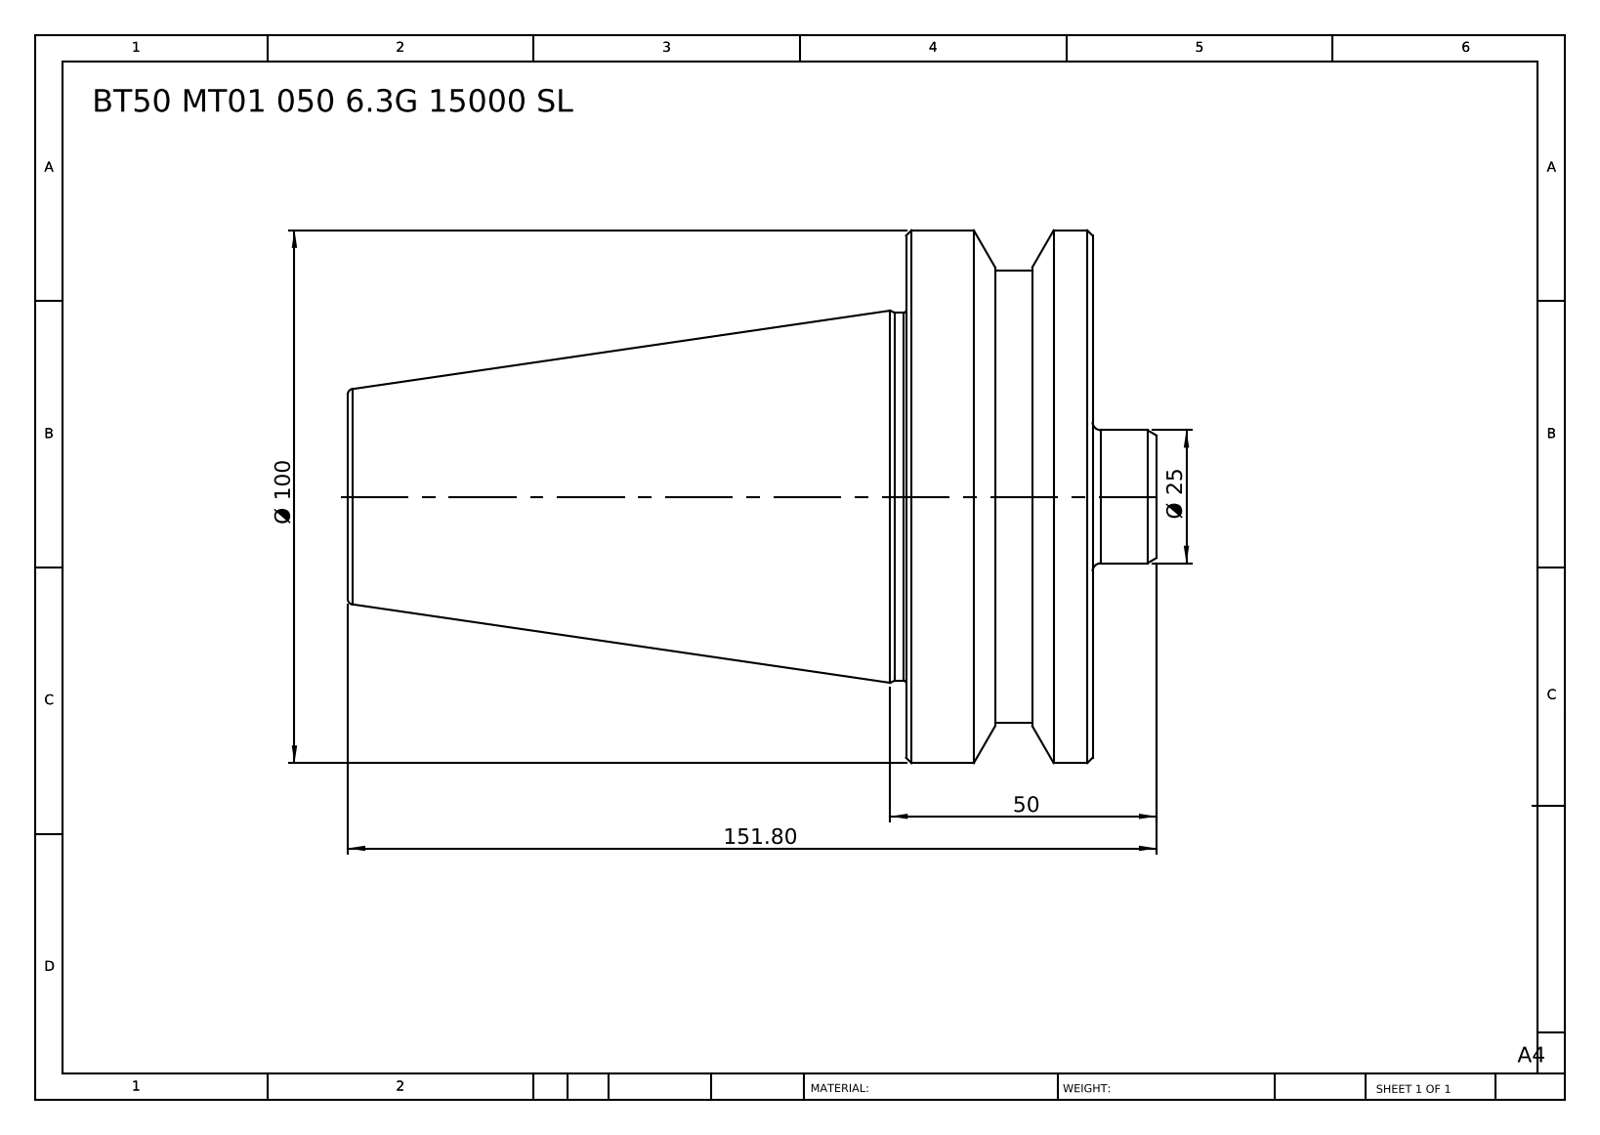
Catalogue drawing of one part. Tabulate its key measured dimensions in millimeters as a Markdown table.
| quantity | value |
| --- | --- |
| part name | BT50 MT01 050 6.3G 15000 SL |
| STEP written by | SolidWorks 2014 (CONFIG_CONTROL_DESIGN) |
| units | millimeters |
| bodies | 1 solid, 36 faces (6 planar, 10 cylindrical, 20 other) |
| overall size | 151.8 × 100 × 100 |
| volume | 515 902 mm³ |
| surface area | 45 199 mm² |
| round bosses / shafts (diameter × count) | 100 × 1, 85 × 1, 69 × 1, 25 × 1 |
| main face-to-face distances | 35, 139.8, 104.8, 12, 47, 151.8, 30.3, 18.3, 16.7, 121.5 |
